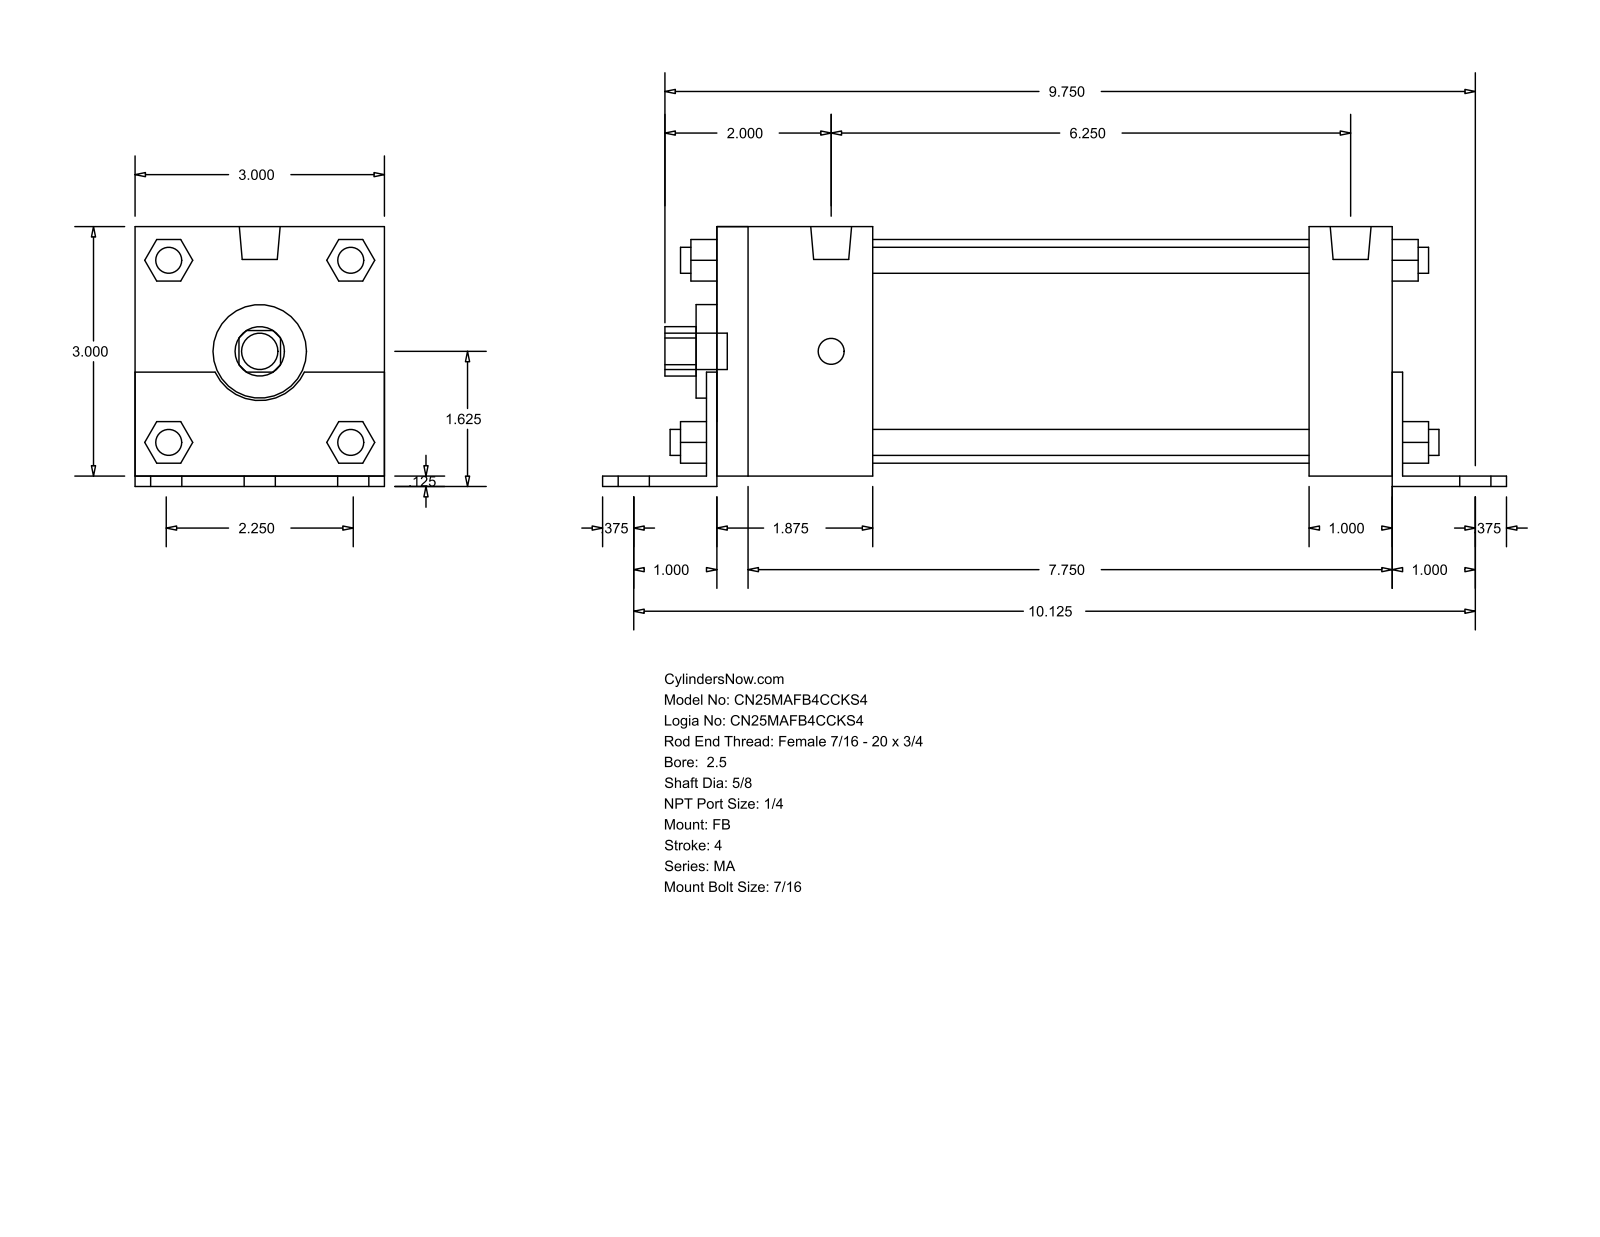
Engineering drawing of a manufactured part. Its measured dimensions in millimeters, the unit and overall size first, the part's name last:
Units: millimetres
Overall size (bounding box): 276.23 × 79.38 × 76.2
Round holes (diameter × count): ⌀15.88 ×1, ⌀28.57 ×1, ⌀68.33 ×1
Round bosses / shafts (diameter × count): ⌀7.94 ×8, ⌀11.11 ×7, ⌀12.49 ×2
Partial cylindrical surfaces — rounded edges, fillets, slot ends (radius × count): R7.54 ×1, R15.05 ×1
Main face-to-face distances: 76.2, 3.17, 79.37, 3.18, 209.55, 206.37, 28.58, 47.62, 25.4, 212.73
Bodies: 0 solids, 140 faces (105 planar, 35 cylindrical, 0 other)
Part name (STEP PRODUCT): MA_FB__0250_0.625
STEP written by: GSSL Pune (CONFIG_CONTROL_DESIGN)
